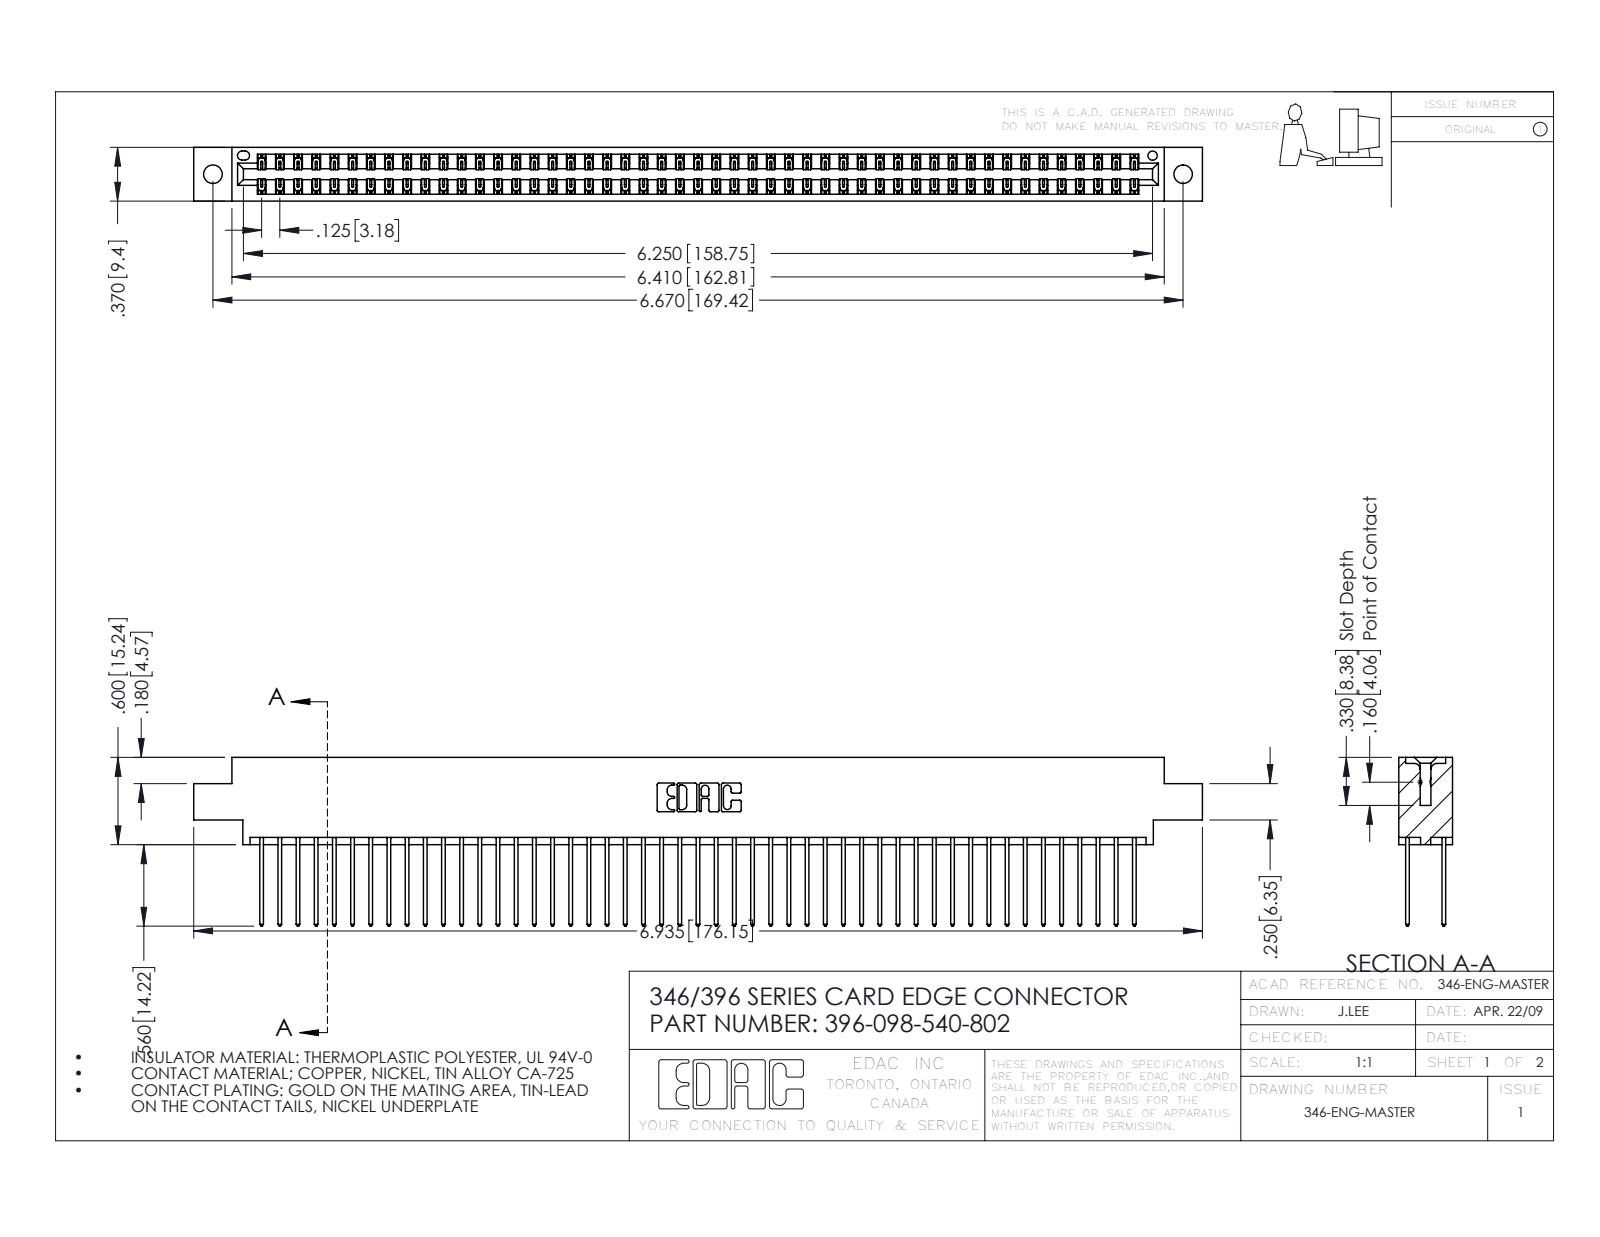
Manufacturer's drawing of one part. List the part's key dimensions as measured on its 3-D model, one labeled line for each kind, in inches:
Part name (STEP PRODUCT): 345-292-001_345-293-140; 396-098-540-802; 346 Part_0.170 Offset - 0.128 Dia
STEP written by: SolidWorks 2016 (CONFIG_CONTROL_DESIGN)
Units: inches
Bodies: 99 solids, 5222 faces (3510 planar, 1712 cylindrical, 0 other)
Overall size (bounding box): 6.935 × 1.16 × 0.37
Volume: 1.063 in³ · Surface area: 39.85 in²
Round holes (diameter × count): ⌀0.128 ×2, ⌀0.064 ×1
Partial cylindrical surfaces — rounded edges, fillets, slot ends (radius × count): R0.006 ×147, R0.01 ×98, R0.01 ×22, R0.007 ×6, R0.031 ×6, R0.026 ×3, R0.014 ×2, R0.022 ×2
Main face-to-face distances: 0.048, 0.322, 0.25, 0.072, 0.298, 0.025, 0.37, 0.275, 0.148, 0.222
Hole centre spacings: 0.246, 6.461, 6.67
